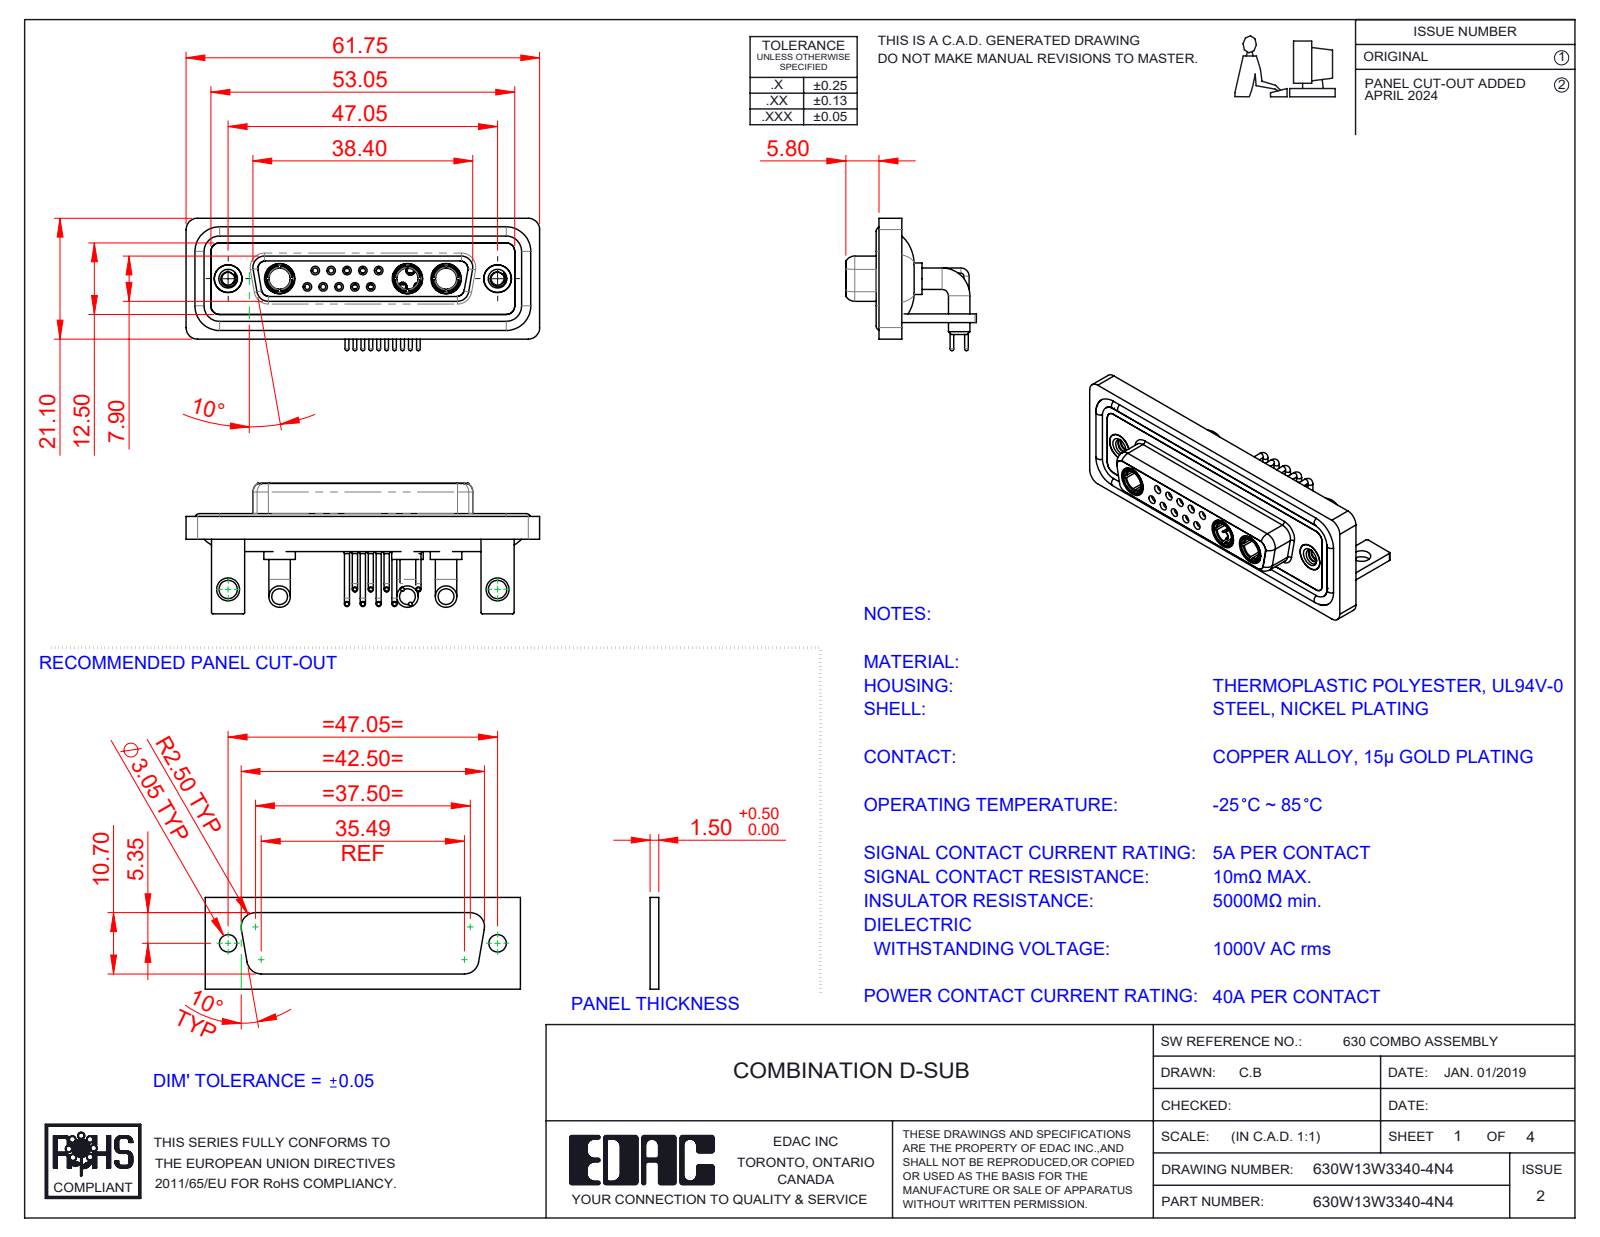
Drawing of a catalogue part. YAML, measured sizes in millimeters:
part_name: "630W13W3340-4N4; 630Combo Shell Rear_25 Contacts; 630Combo Contact Row 2_50 Contacts; 630Combo Housing_13W3 (+6 more)"
step_written_by: "SolidWorks 2023 (CONFIG_CONTROL_DESIGN)"
units: millimeters
bodies: {solids: 25, faces: 1198, planar: 362, cylindrical: 517, other: 319}
overall_size: [61.75, 23.12, 22.8]
volume: 9055
surface_area: 15163
round_holes:
  - {diameter: 0.9, count: 10}
  - {diameter: 1.1, count: 10}
  - {diameter: 1.5, count: 10}
  - {diameter: 2, count: 10}
  - {diameter: 1.6, count: 5}
  - {diameter: 1.7, count: 5}
  - {diameter: 4.85, count: 5}
  - {diameter: 3.7, count: 3}
  - {diameter: 5.3, count: 3}
  - {diameter: 2.26, count: 2}
  - {diameter: 3.2, count: 2}
  - {diameter: 4, count: 2}
round_bosses_or_shafts:
  - {diameter: 0.9, count: 15}
  - {diameter: 1.6, count: 12}
  - {diameter: 0.65, count: 10}
  - {diameter: 3.75, count: 6}
  - {diameter: 2, count: 5}
  - {diameter: 1.5, count: 5}
  - {diameter: 5.5, count: 3}
  - {diameter: 5.2, count: 3}
partial_cylinders:
  - {radius: 2, count: 19}
  - {radius: 1.5, count: 18}
  - {radius: 0.25, count: 16}
  - {radius: 1.35, count: 8}
  - {radius: 1.6, count: 8}
  - {radius: 0.5, count: 5}
  - {radius: 0.6, count: 4}
  - {radius: 0.65, count: 4}
face_to_face_distances: [0.4, 1.8, 2.9, 3.7, 1.5, 4.1, 1.1, 1.4, 1.6, 3.1]
hole_center_spacings: [3.16, 2.77, 5.54, 5.04, 8.31, 5.03, 7.49, 11.08]
